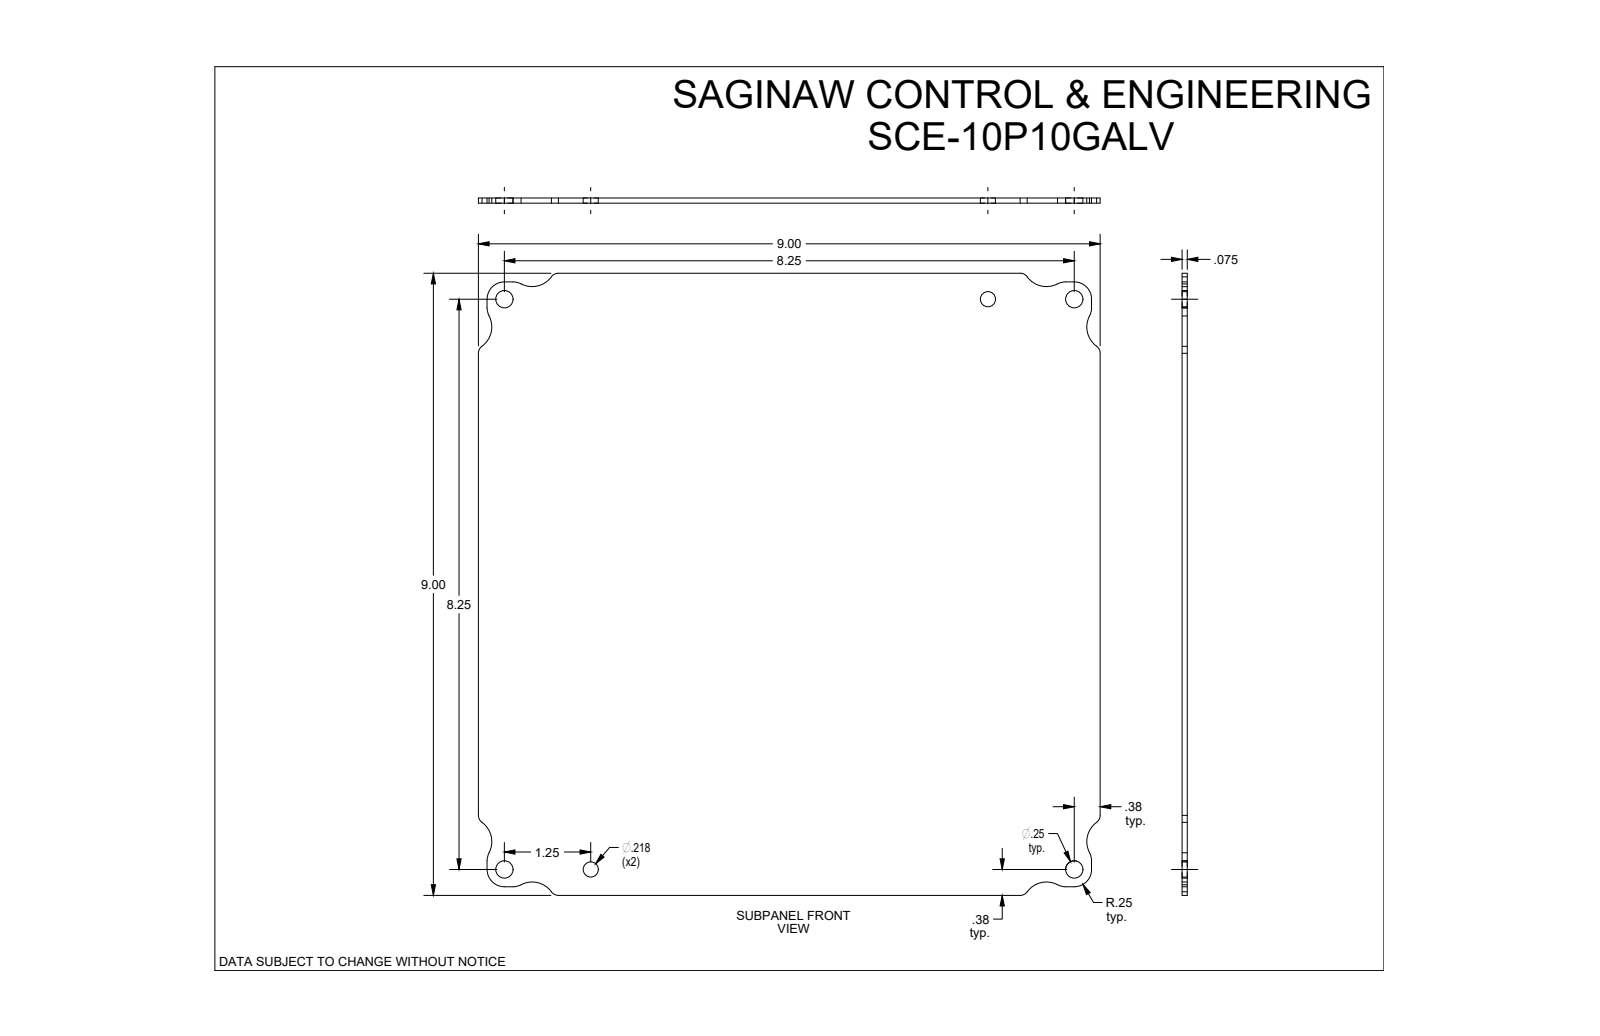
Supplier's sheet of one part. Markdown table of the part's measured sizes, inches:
| quantity | value |
| --- | --- |
| part name | SCE-10P10GALV |
| STEP written by | SolidWorks 2019 (CONFIG_CONTROL_DESIGN) |
| units | inches |
| bodies | 1 solid, 48 faces (14 planar, 34 cylindrical, 0 other) |
| overall size | 9 × 9 × 0.075 |
| volume | 5.965 in³ |
| surface area | 162 in² |
| round holes (diameter × count) | 0.25 × 4, 0.218 × 2 |
| partial cylindrical surfaces (radius × count) | 0.25 × 12, 0.125 × 8, 0.344 × 8 |
| main face-to-face distances | 0.075, 9, 0.125, 8.875, 8.75 |
| hole center spacings | 8.25, 1.25, 7, 8.344, 10.819, 11.667, 10.056 |
